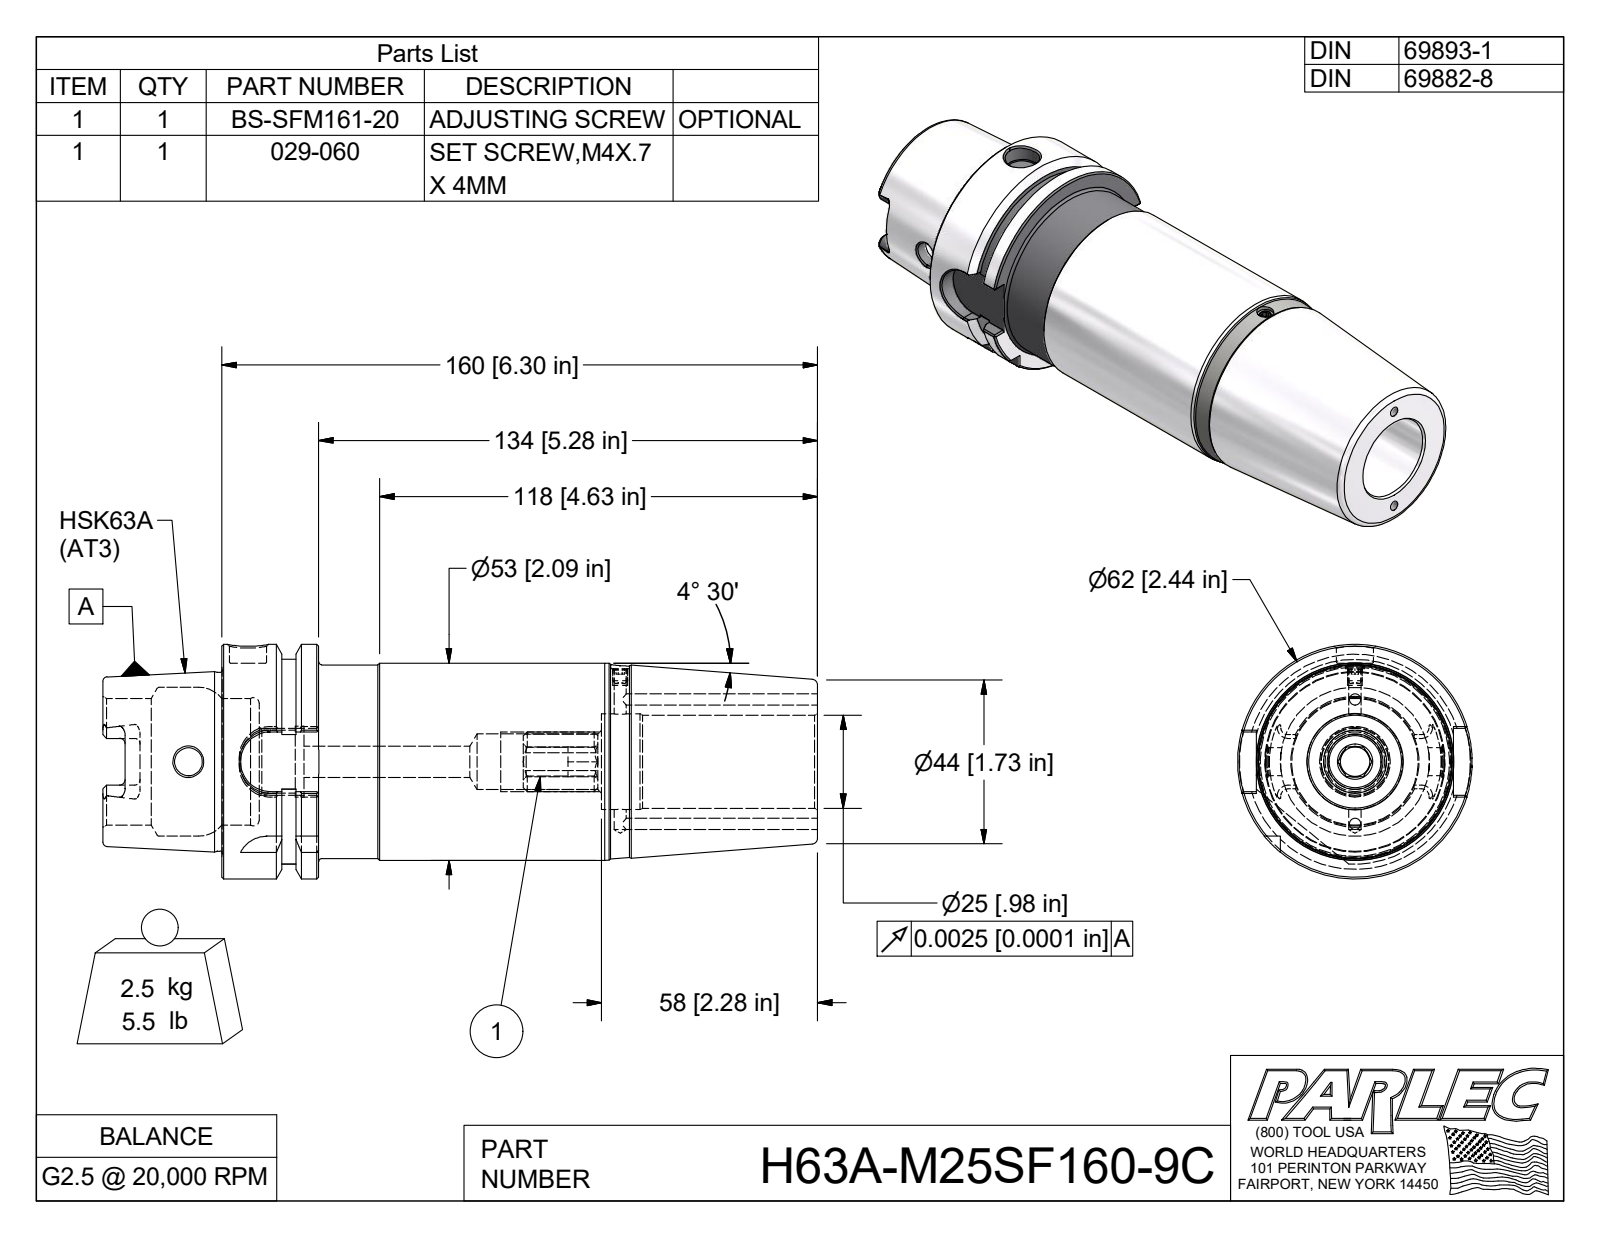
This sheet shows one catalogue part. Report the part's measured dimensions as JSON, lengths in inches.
{"part_name": "H63A-M25SF160-9C", "step_written_by": "Autodesk Inventor 2018 (AUTOMOTIVE_DESIGN)", "units": "inches", "bodies": {"solids": 1, "faces": 159, "planar": 63, "cylindrical": 43, "other": 53}, "overall_size": [7.559, 2.48, 2.48], "volume_in3": 19.34, "surface_area_in2": 80, "round_holes": [[0.118, 2], [0.128, 1], [0.197, 1], [0.295, 1], [0.331, 1], [0.394, 1], [0.587, 1], [0.666, 1], [0.749, 1], [0.983, 1], [1.013, 1], [1.339, 1]], "round_bosses_or_shafts": [[2.48, 1], [2.087, 1], [2.047, 1], [1.891, 1]], "partial_cylinders_radius": [[0.059, 6], [0.113, 4], [0.315, 4], [1.083, 1]], "face_to_face_distances": [5.276, 6.299, 1.024, 2.283, 0.241, 0.389, 0.394, 0.63, 5.906, 1.26], "hole_center_spacings": [0.658, 1.316, 3.937]}
